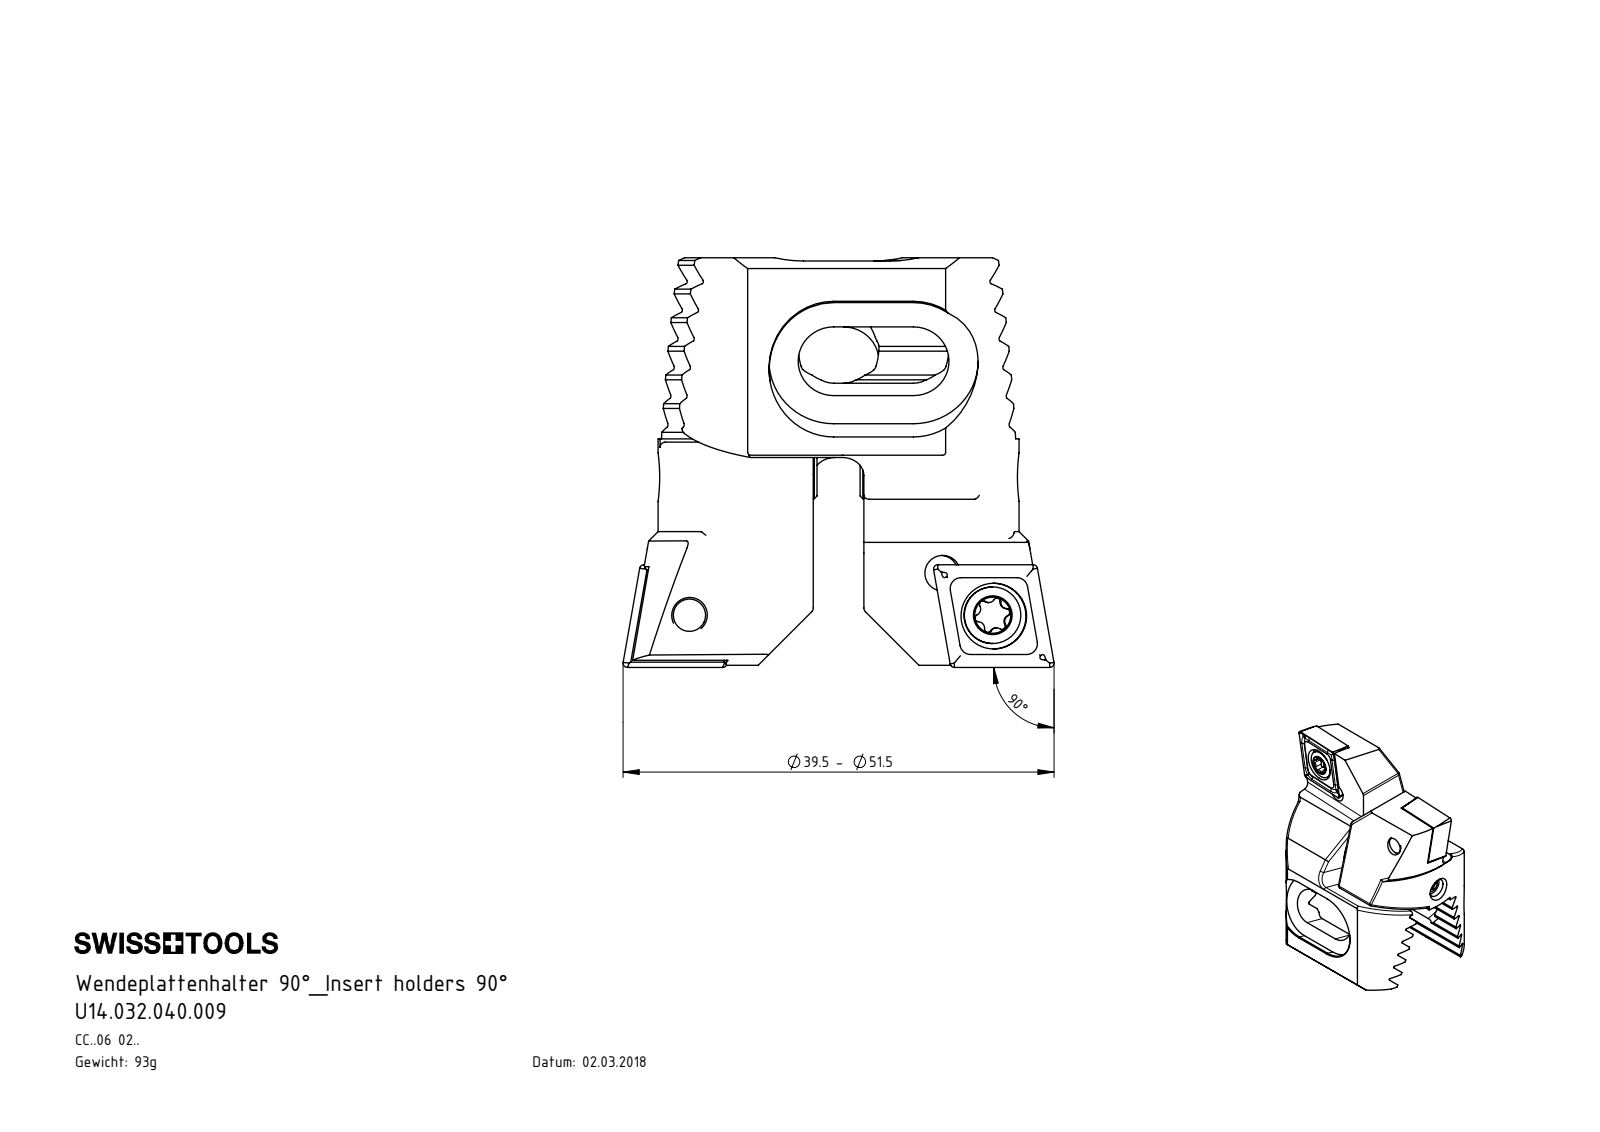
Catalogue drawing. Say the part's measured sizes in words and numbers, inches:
The part is named "Z32-xxx.001.021_B; Z32-ER3.001.013_A; Z32.WCB.B11.021; CCMT09T304 (+1 more)". Its 3-D file was written by "SolidWorks 2017 (AUTOMOTIVE_DESIGN)". It is 8 solids with 404 faces: 182 planar, 102 cylindrical and 120 other. Overall it measures 1.575 by 1.496 by 1.031 inches. Its volume is 0.724 cubic inches and its surface area 12.8 square inches. Round holes: 4 of diameter 0.13, 2 of diameter 0.063, 2 of diameter 0.173, 2 of diameter 0.24, 1 of diameter 0.079, 1 of diameter 0.138. Round bosses or shafts: 3 of diameter 0.157, 2 of diameter 0.207. Partial cylindrical surfaces (rounded edges, fillets, slot ends): 16 of radius 0.02, 12 of radius 0.008, 12 of radius 0.013, 12 of radius 0.023, 4 of radius 0.079, 4 of radius 0.13, 4 of radius 0.236, 4 of radius 0.472. The main face-to-face distances are 0.094, 0.187, 0.375, 0.281, 0.193, 0.469, 0.281, 0.05, 0.188, 0.094. The hole center spacings are 0.239, 0.244, 0.354, 0.954, 0.958, 1.128, 0.684, 0.759.
